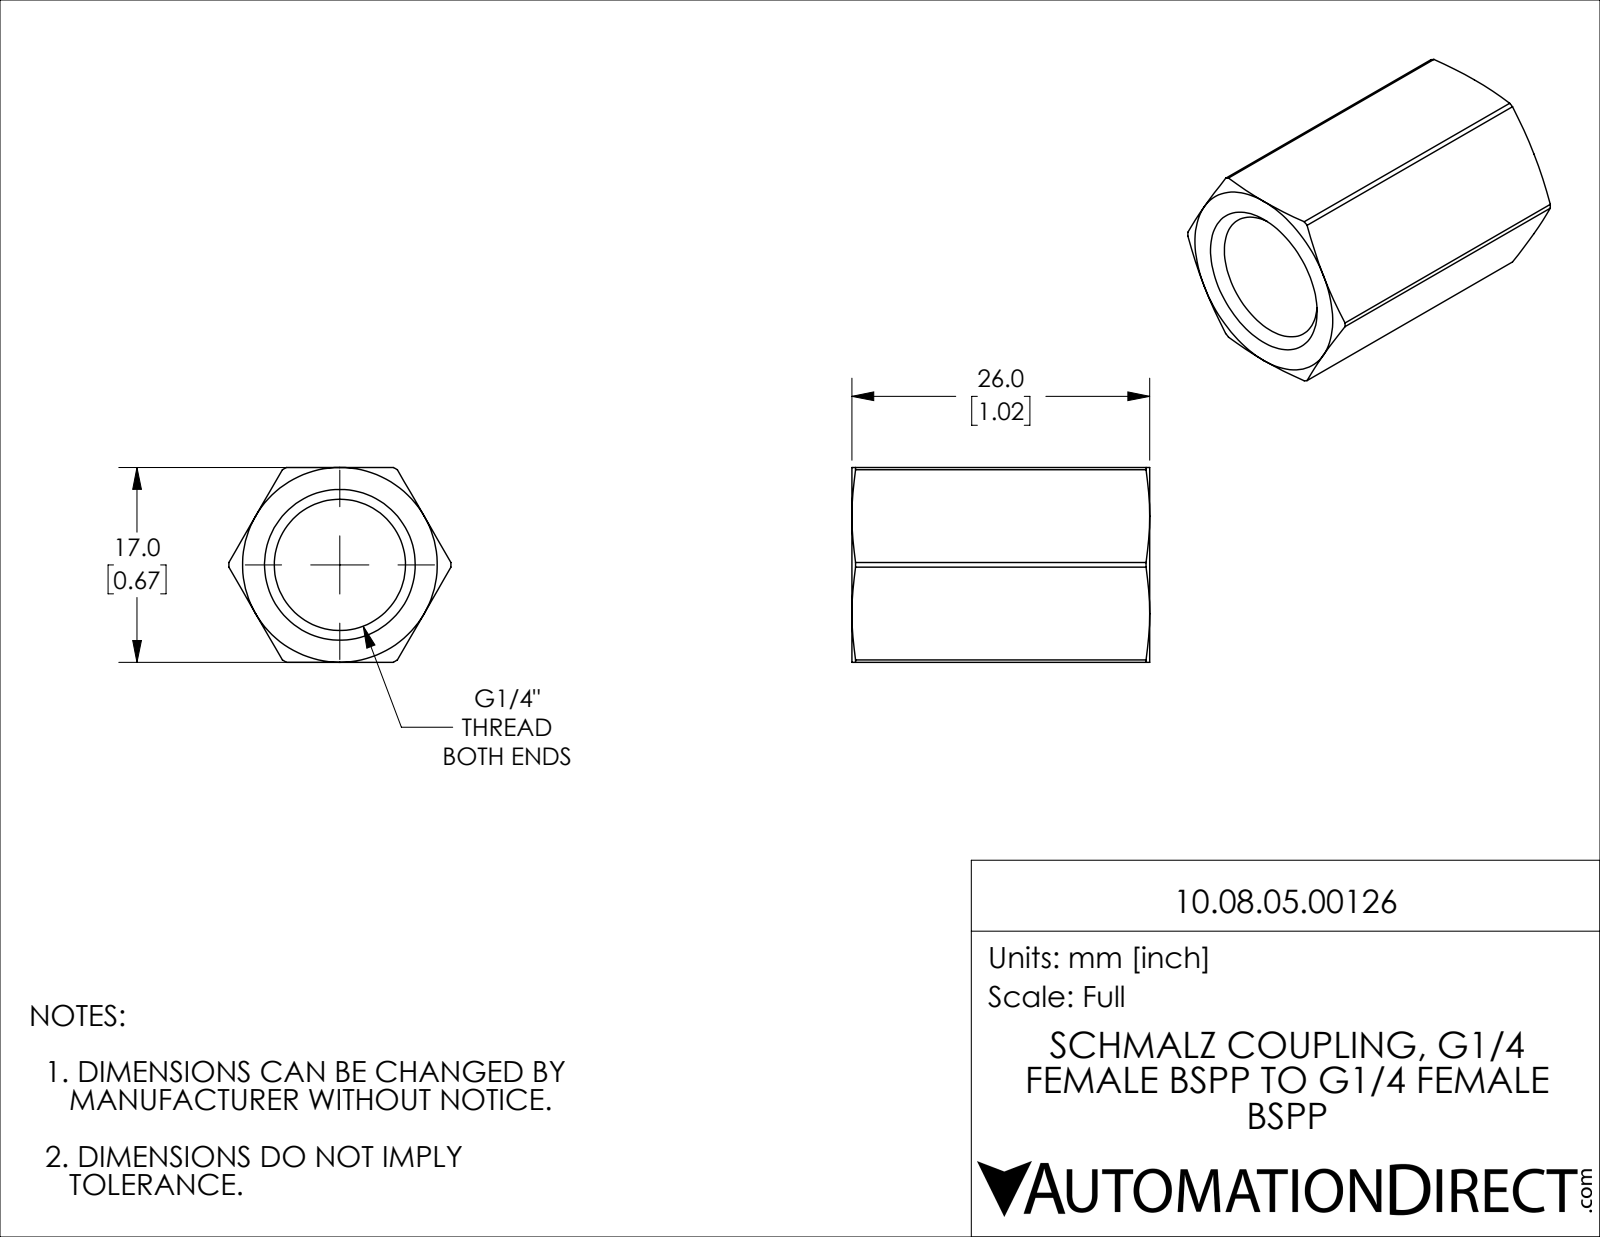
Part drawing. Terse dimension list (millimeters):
name: 10.08.05.00126
written by: SolidWorks 2021 (CONFIG_CONTROL_DESIGN)
unit: mm
bodies: 1 solid, 34 faces (8 planar, 10 cylindrical, 16 other)
size: 26 × 19.4 × 17
volume: 3 794 mm³; area: 2 705 mm²
holes: 1× ⌀11.45
rounds: 1× R9.7
face distances: 17, 26
